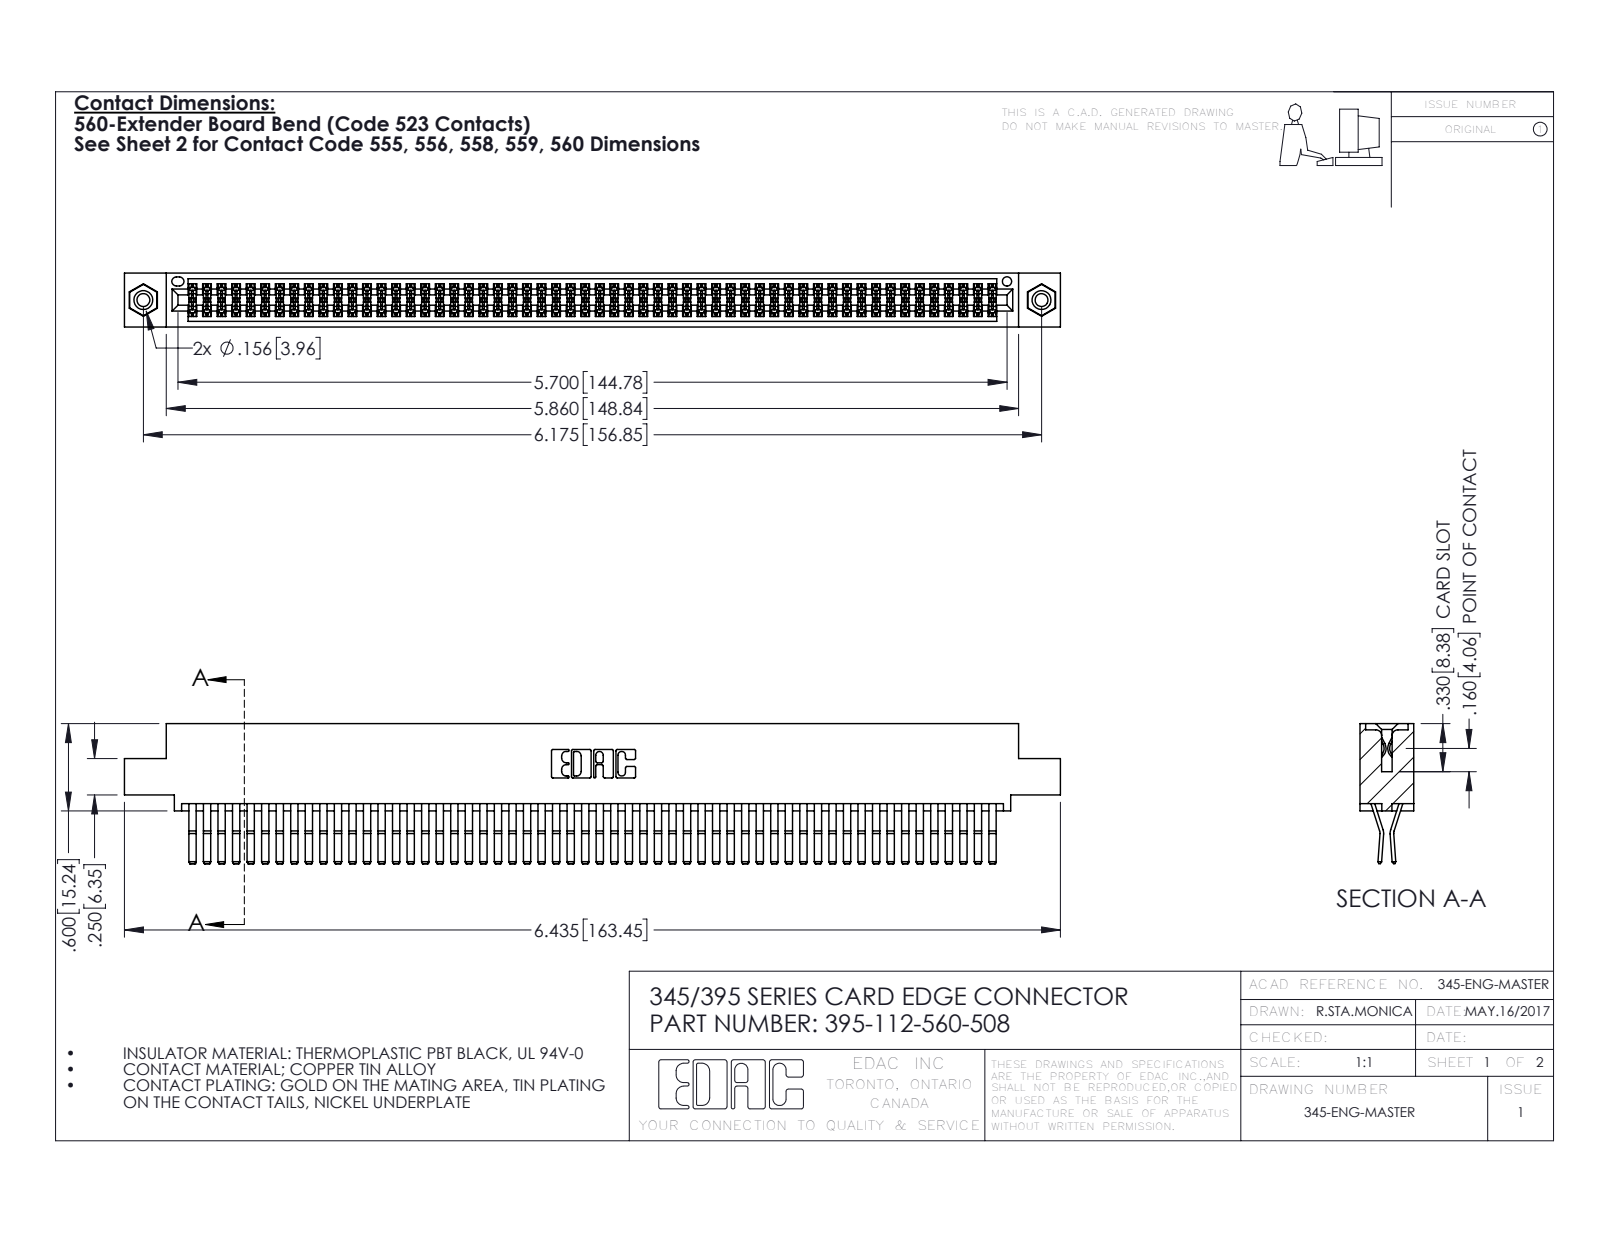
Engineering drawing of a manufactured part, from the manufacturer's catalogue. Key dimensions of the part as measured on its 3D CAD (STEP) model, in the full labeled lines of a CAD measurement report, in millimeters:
Part name (STEP PRODUCT): 345-250-001_345-250-003-102; 395-112-560-508; 345 Part_0.110 Offset - 0.156 Dia-TI; 345-292-001_560 Tail
STEP written by: SolidWorks 2016 (CONFIG_CONTROL_DESIGN)
Units: millimetres
Bodies: 115 solids, 6014 faces (3812 planar, 2186 cylindrical, 16 other)
Overall size (bounding box): 163.4 × 24.4 × 9.4
Volume: 16 670 mm³ · Surface area: 26 900 mm²
Round holes (diameter × count): ⌀2.3 ×2, ⌀3.2 ×2, ⌀4 ×2, ⌀1.6 ×1
Round bosses / shafts (diameter × count): ⌀3.9 ×2
Partial cylindrical surfaces — rounded edges, fillets, slot ends (radius × count): R0.2 ×168, R0.3 ×22, R0.2 ×6, R0.8 ×6, R0.7 ×3, R0.3 ×2, R0.4 ×2, R0.5 ×2
Main face-to-face distances: 0.6, 1.8, 7.6, 9.4, 5.1, 2.5, 6.9, 5.7, 4.4, 3.8
Hole centre spacings: 6.9, 150.9, 156.8
